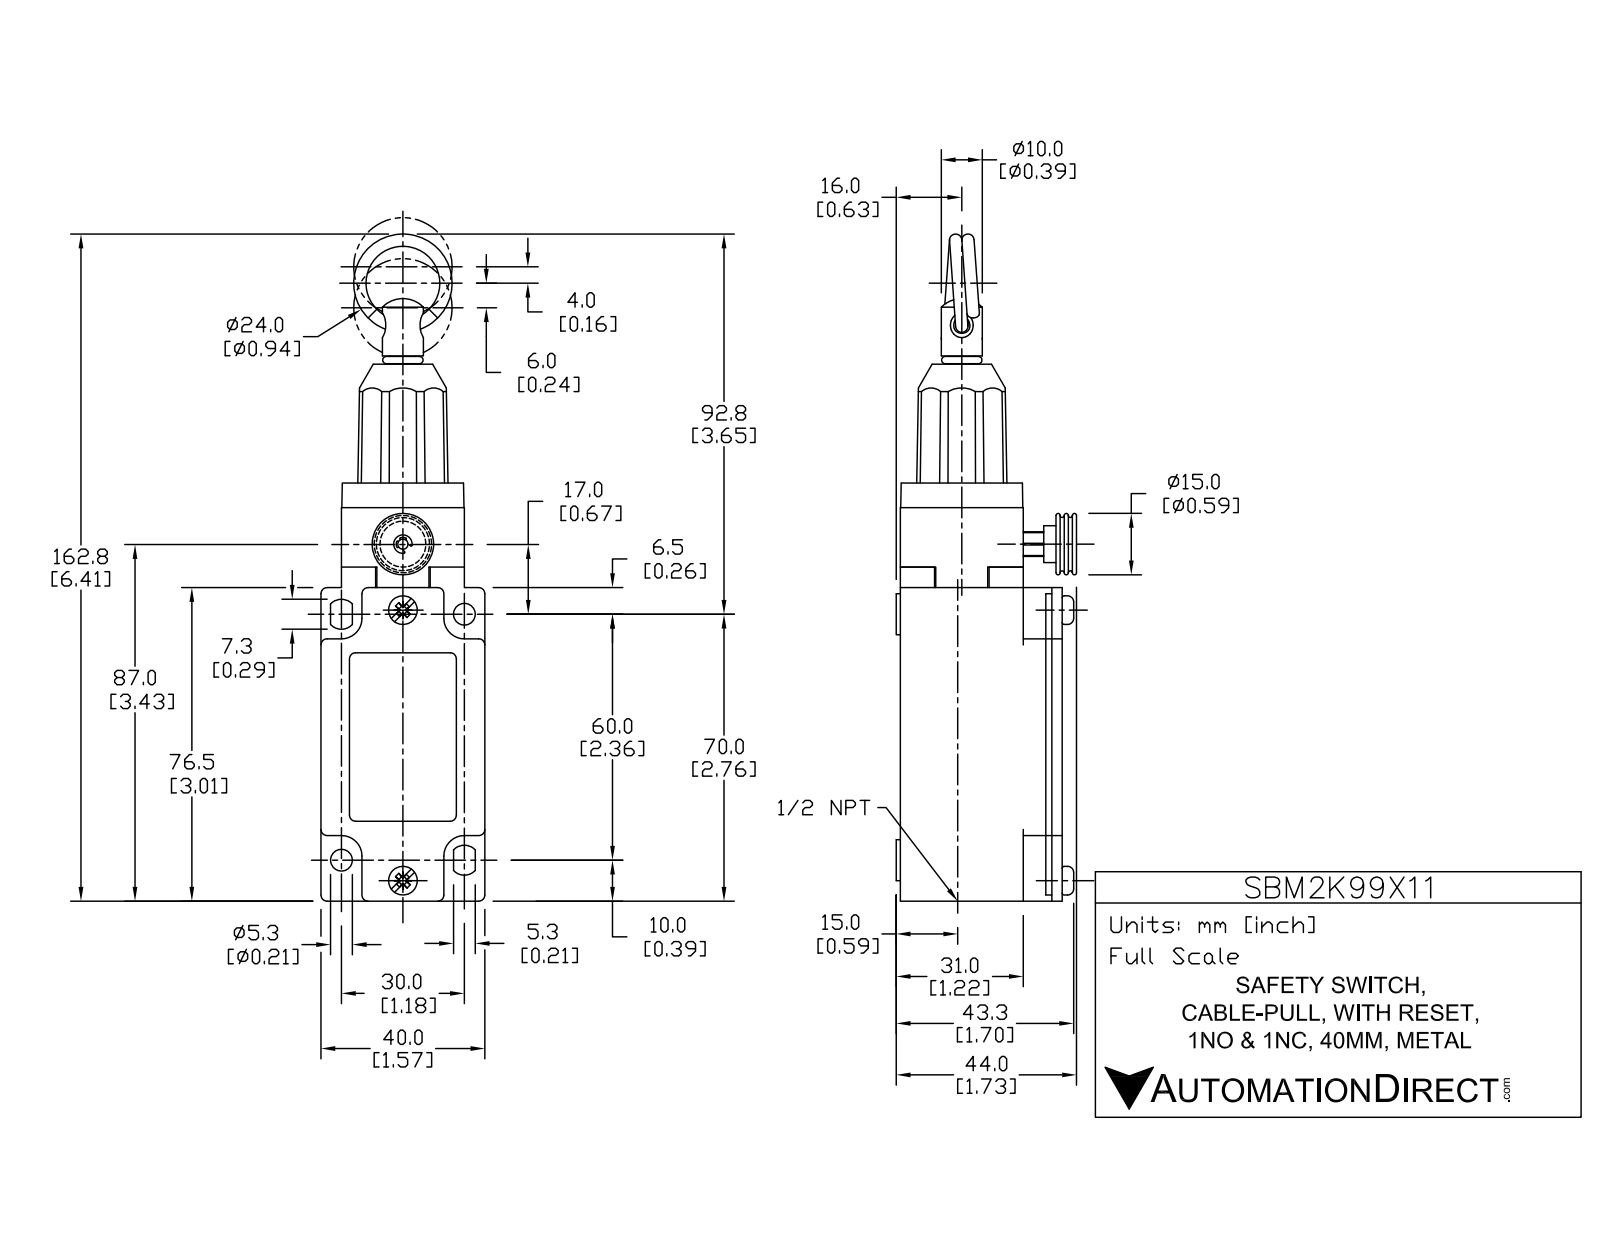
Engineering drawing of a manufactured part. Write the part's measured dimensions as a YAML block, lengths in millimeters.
part_name: "SBM2K99X11"
step_written_by: "SolidWorks 2017 (AUTOMOTIVE_DESIGN)"
units: millimeters
bodies: {solids: 5, faces: 233, planar: 91, cylindrical: 88, other: 54}
overall_size: [164, 43.8, 40]
volume: 142500
surface_area: 30610
round_holes:
  - {diameter: 5.2, count: 2}
  - {diameter: 4, count: 1}
  - {diameter: 10.1, count: 1}
  - {diameter: 17, count: 1}
  - {diameter: 18, count: 1}
  - {diameter: 19, count: 1}
round_bosses_or_shafts:
  - {diameter: 10, count: 5}
  - {diameter: 7, count: 2}
  - {diameter: 17.8, count: 1}
  - {diameter: 9.8, count: 1}
  - {diameter: 6.7, count: 1}
  - {diameter: 6.3, count: 1}
  - {diameter: 2.5, count: 1}
partial_cylinders:
  - {radius: 1.5, count: 16}
  - {radius: 5, count: 4}
  - {radius: 3.3, count: 2}
  - {radius: 11.5, count: 1}
  - {radius: 12, count: 1}
face_to_face_distances: [40, 5, 30, 39.5, 35, 9.5, 76.5, 1, 26, 25]
hole_center_spacings: [1, 67.1]
